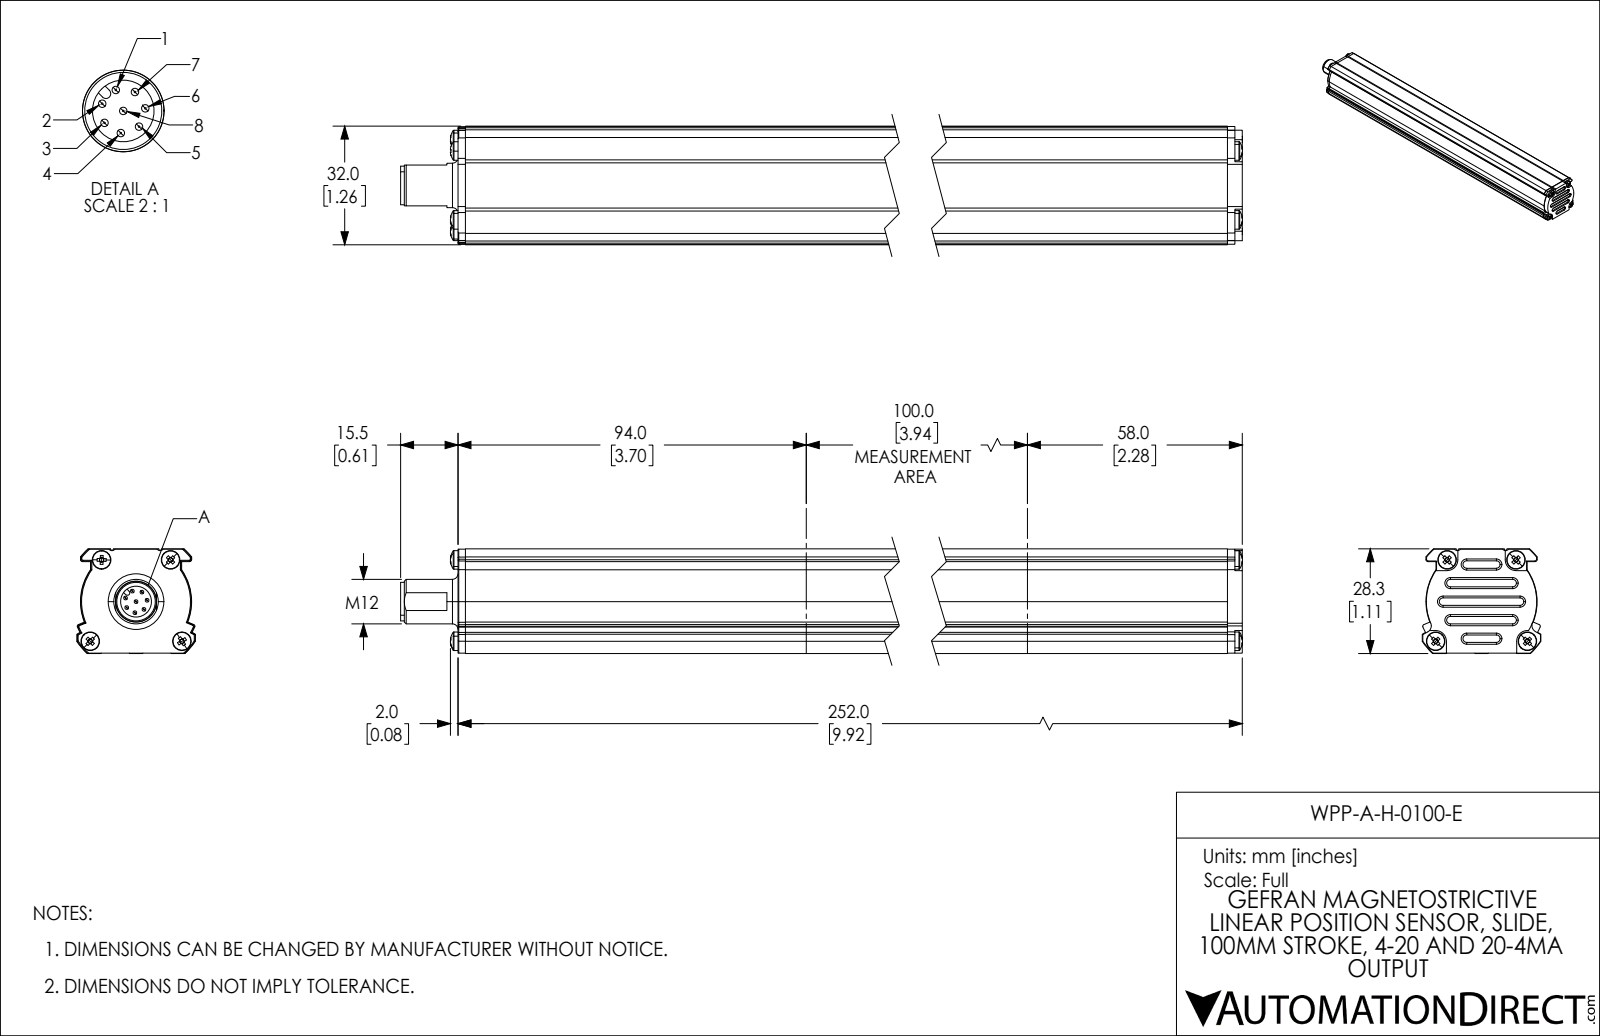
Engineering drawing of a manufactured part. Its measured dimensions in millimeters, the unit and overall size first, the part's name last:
Units: millimetres
Overall size (bounding box): 267.55 × 32 × 28.25
Round holes (diameter × count): ⌀2.6 ×5, ⌀2.3 ×4, ⌀7 ×1, ⌀8.3 ×1, ⌀9.4 ×1
Round bosses / shafts (diameter × count): ⌀1 ×8, ⌀5 ×5, ⌀12 ×1, ⌀10.4 ×1, ⌀9.55 ×1, ⌀8 ×1
Partial cylindrical surfaces — rounded edges, fillets, slot ends (radius × count): R0.5 ×8, R2.9 ×4, R0.4 ×2, R1 ×2, R1.85 ×2, R0.65 ×1, R2 ×1, R14.9 ×1
Main face-to-face distances: 28, 28.25, 246, 2, 24.8, 24.55, 3.45, 3.7, 28.3, 248
Hole centre spacings: 16.36, 14.6, 22.17, 30.85, 18.6, 22.16, 24.75, 24.76
Volume: 201 518 mm³ · Surface area: 45 965 mm²
Bodies: 20 solids, 605 faces (301 planar, 131 cylindrical, 173 other)
Part name (STEP PRODUCT): WPP-A-H-0100-E
STEP written by: SolidWorks 2021 (CONFIG_CONTROL_DESIGN)
